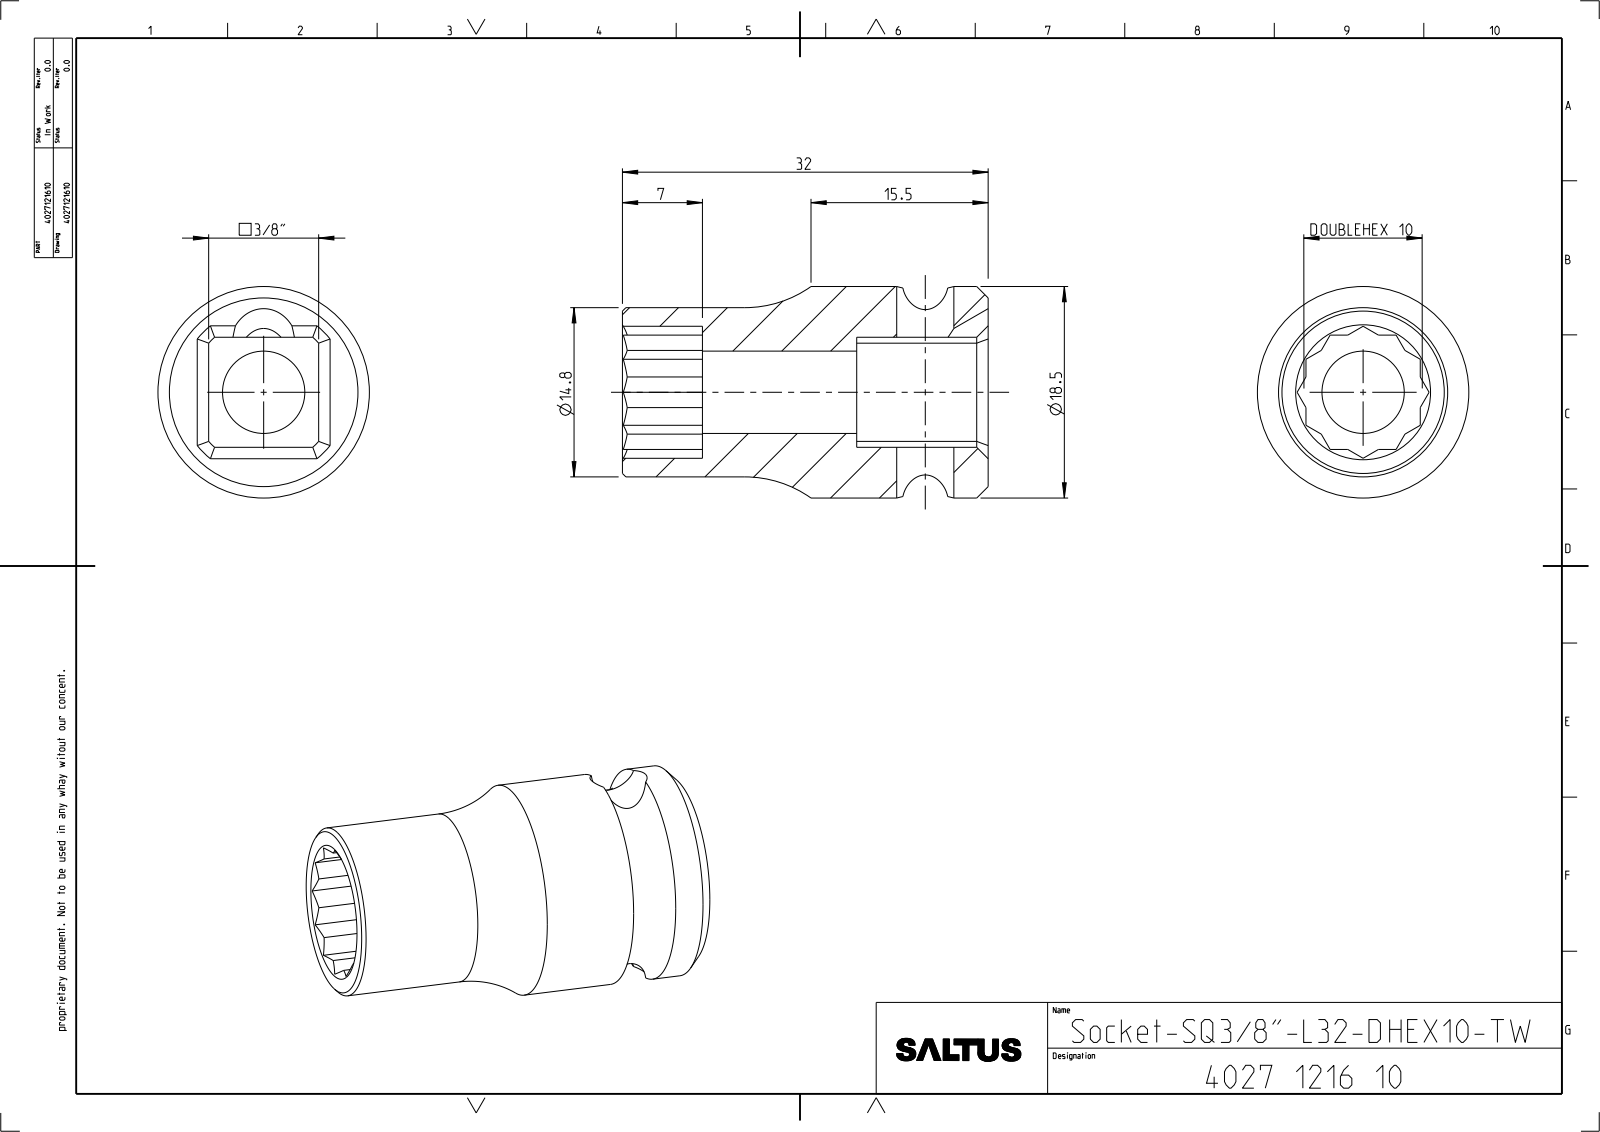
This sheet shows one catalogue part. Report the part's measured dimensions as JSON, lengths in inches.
{"part_name": "4027121610", "step_written_by": "CREO PARAMETRIC BY PTC INC, 2022414 (CONFIG_CONTROL_DESIGN)", "units": "inches", "bodies": {"solids": 1, "faces": 68, "planar": 37, "cylindrical": 17, "other": 14}, "overall_size": [1.26, 0.728, 0.728], "volume_in3": 0.273, "surface_area_in2": 4.752, "round_holes": [[0.197, 1], [0.283, 1]], "round_bosses_or_shafts": [[0.728, 1], [0.583, 1]], "partial_cylinders_radius": [[0.118, 1], [0.254, 1]], "face_to_face_distances": [0.379, 0.394, 0.386, 0.984, 0.453, 0.531, 1.26, 0.807, 0.276]}
